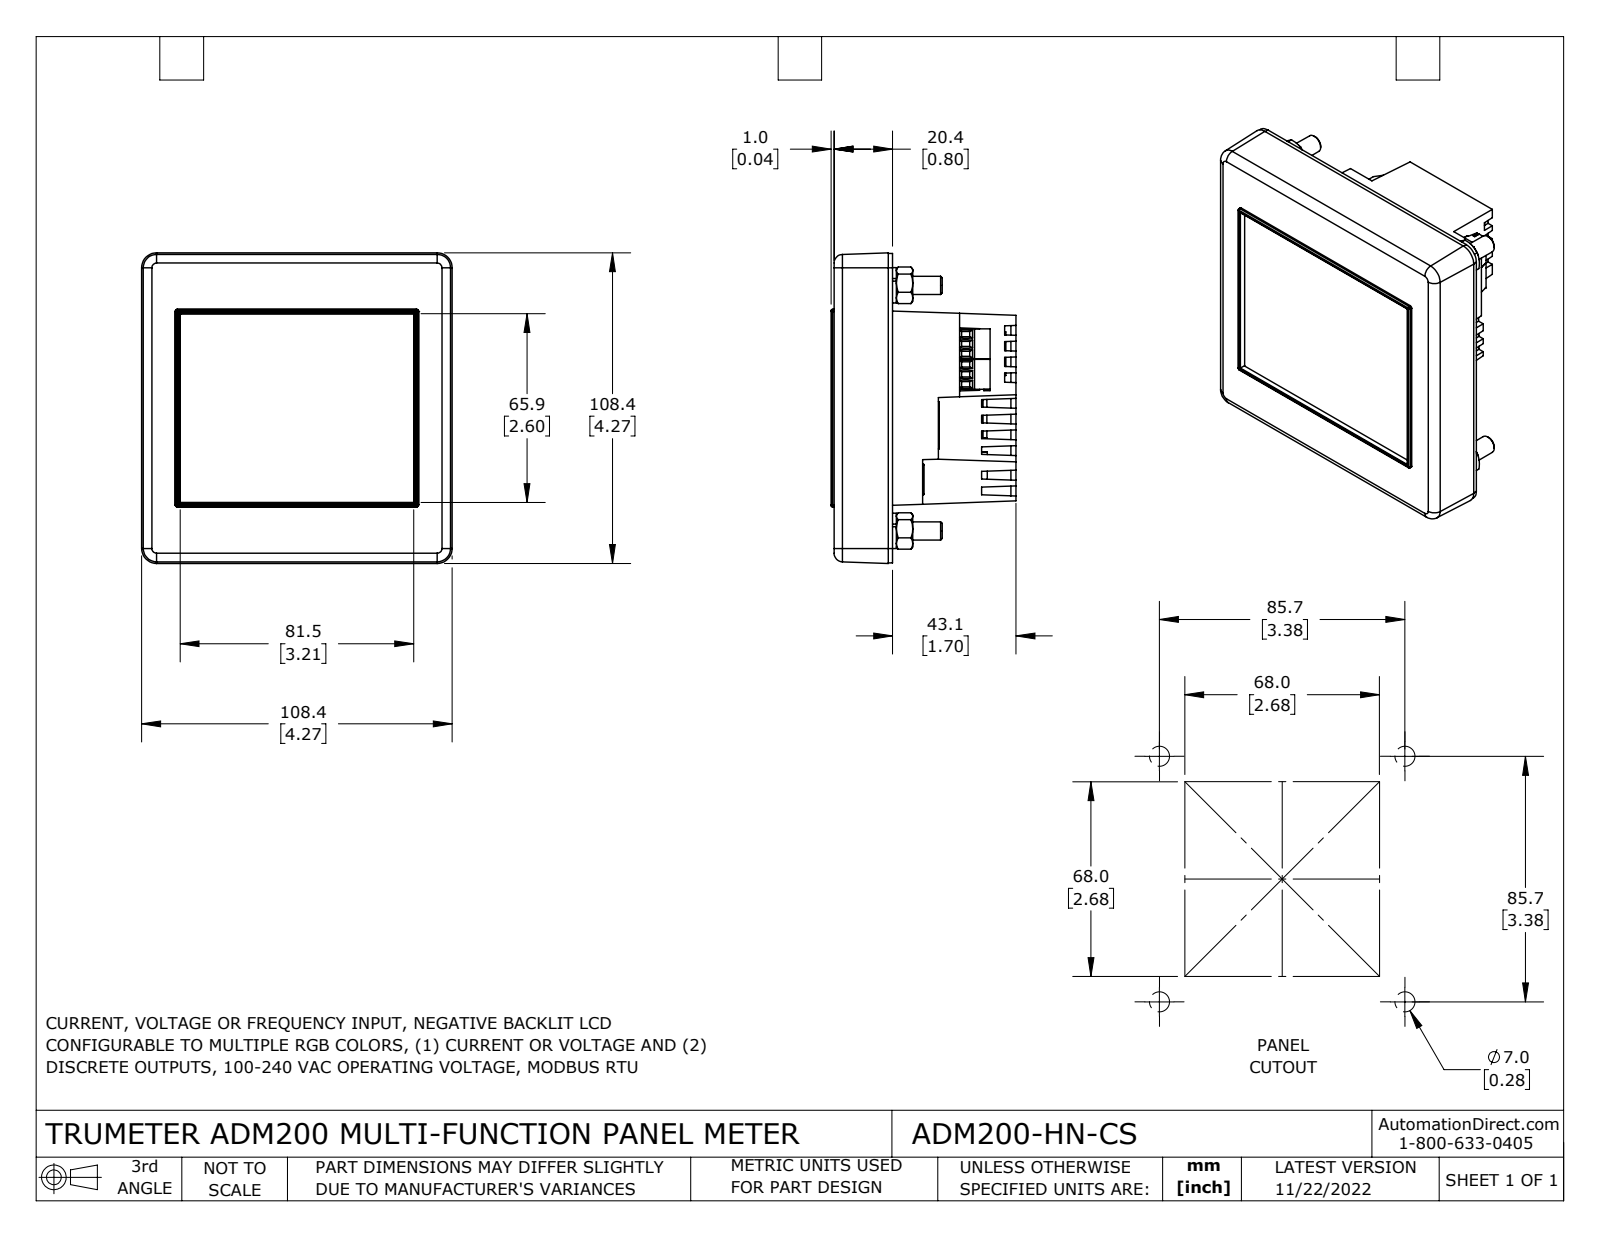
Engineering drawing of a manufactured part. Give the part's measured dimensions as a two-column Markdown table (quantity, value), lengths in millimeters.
| quantity | value |
| --- | --- |
| part name | ADM200-HN-CS |
| STEP written by | SolidWorks 2021 (CONFIG_CONTROL_DESIGN) |
| units | millimeters |
| bodies | 23 solids, 2059 faces (1384 planar, 290 cylindrical, 385 other) |
| overall size | 108.4 × 108.4 × 64.5 |
| volume | 128 000 mm³ |
| surface area | 123 100 mm² |
| round holes (diameter × count) | 1.8 × 9, 2.9 × 6, 3 × 5, 5.4 × 4, 6.4 × 4, 6.6 × 4, 7.5 × 4, 3.9 × 2 |
| round bosses / shafts (diameter × count) | 1 × 5, 12.4 × 4, 11.1 × 4, 0.6 × 4, 2 × 2 |
| partial cylindrical surfaces (radius × count) | 0.2 × 32, 0.5 × 30, 1 × 7, 0.4 × 4, 0.8 × 4, 3 × 4, 5 × 4, 0.1 × 2 |
| main face-to-face distances | 0.8, 16.1, 2.8, 1.9, 1.5, 2, 17.6, 86.2, 88.1, 1.2 |
| hole center spacings | 18, 82, 3.5, 7.4, 25, 36, 54, 60.9 |
